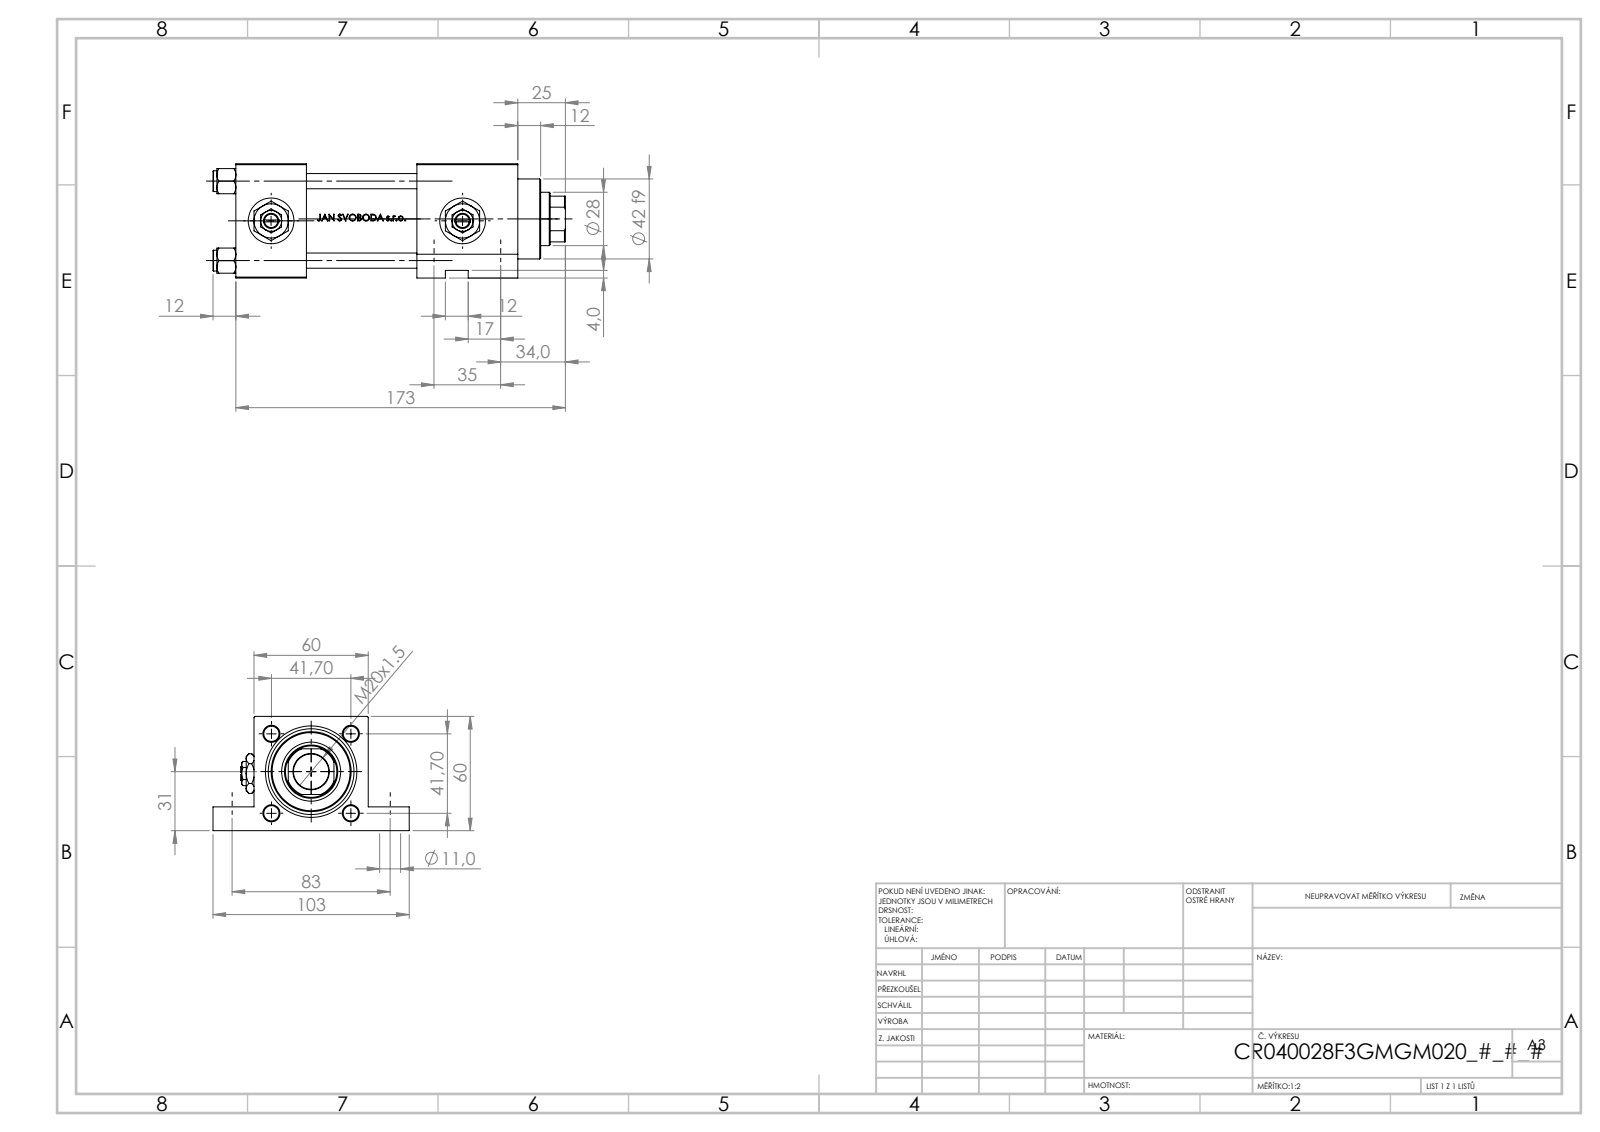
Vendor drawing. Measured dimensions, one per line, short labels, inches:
name: V215CR_F_Body; NUT_M5_F; V215CR_VCP_F; Zatka_pro_OIL_PORT (+2 more)
written by: SolidWorks 2019 (CONFIG_CONTROL_DESIGN)
unit: in
bodies: 12 solids, 1216 faces (486 planar, 148 cylindrical, 582 other)
size: 7.283 × 4.055 × 2.362
volume: 10.14 in³; area: 181.7 in²
holes: 4× ⌀0.315, 4× ⌀0.433, 3× ⌀0.656, 3× ⌀0.945, 2× ⌀0.098, 2× ⌀0.276, 1× ⌀0.63, 1× ⌀0.728, 1× ⌀1.102, 1× ⌀1.22, 1× ⌀1.772
bosses: 4× ⌀0.433, 1× ⌀1.811, 1× ⌀1.654, 1× ⌀1.575
rounds: 1× R0.531
face distances: 2.362, 3.74, 1.457, 5.827, 2.283, 2.087, 4.37, 1.496, 1.87, 0.492
hole spacings: 0.821, 1.161, 1.642, 1.832, 0.817, 1.378, 2.322, 3.268
